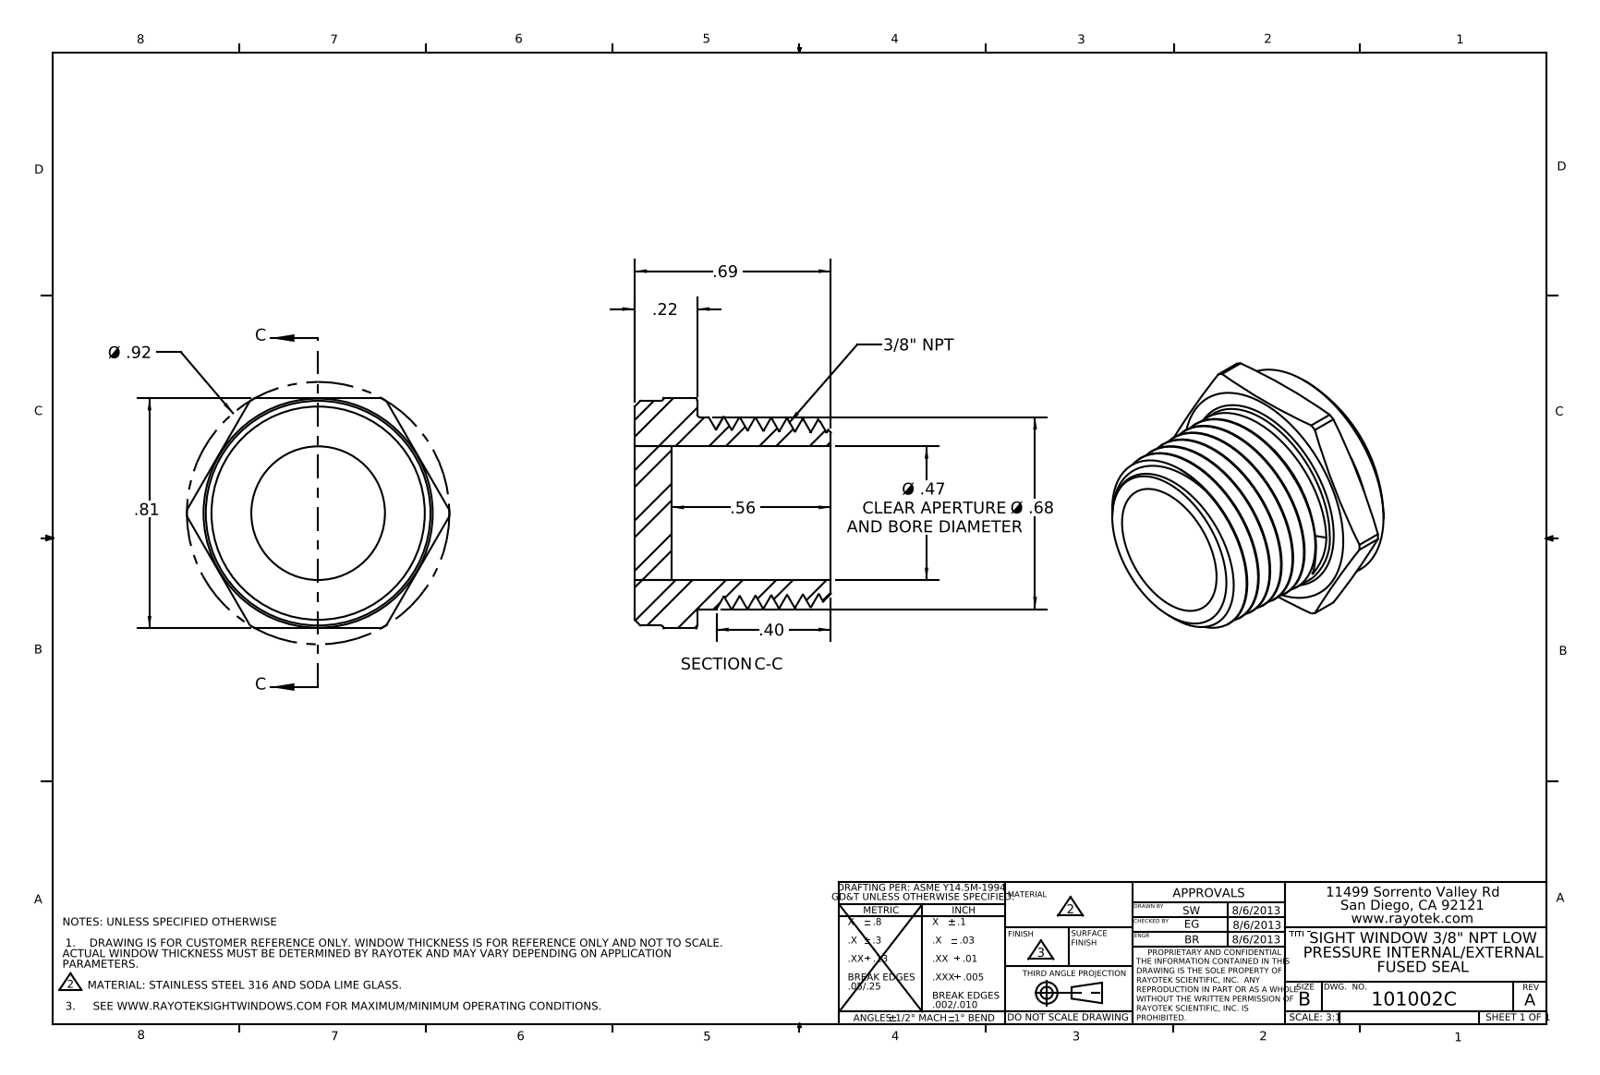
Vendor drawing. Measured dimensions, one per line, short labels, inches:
name: 403002
written by: SolidWorks 2012 (AUTOMOTIVE_DESIGN)
unit: in
bodies: 2 solids, 59 faces (14 planar, 16 cylindrical, 29 other)
size: 0.923 × 0.81 × 0.69
volume: 0.165 in³; area: 4.391 in²
holes: 1× ⌀0.47
bosses: 1× ⌀0.79, 1× ⌀0.675
rounds: 1× R0.462
face distances: 0.13, 0.81, 0.22, 0.09, 0.69, 0.56, 0.47
